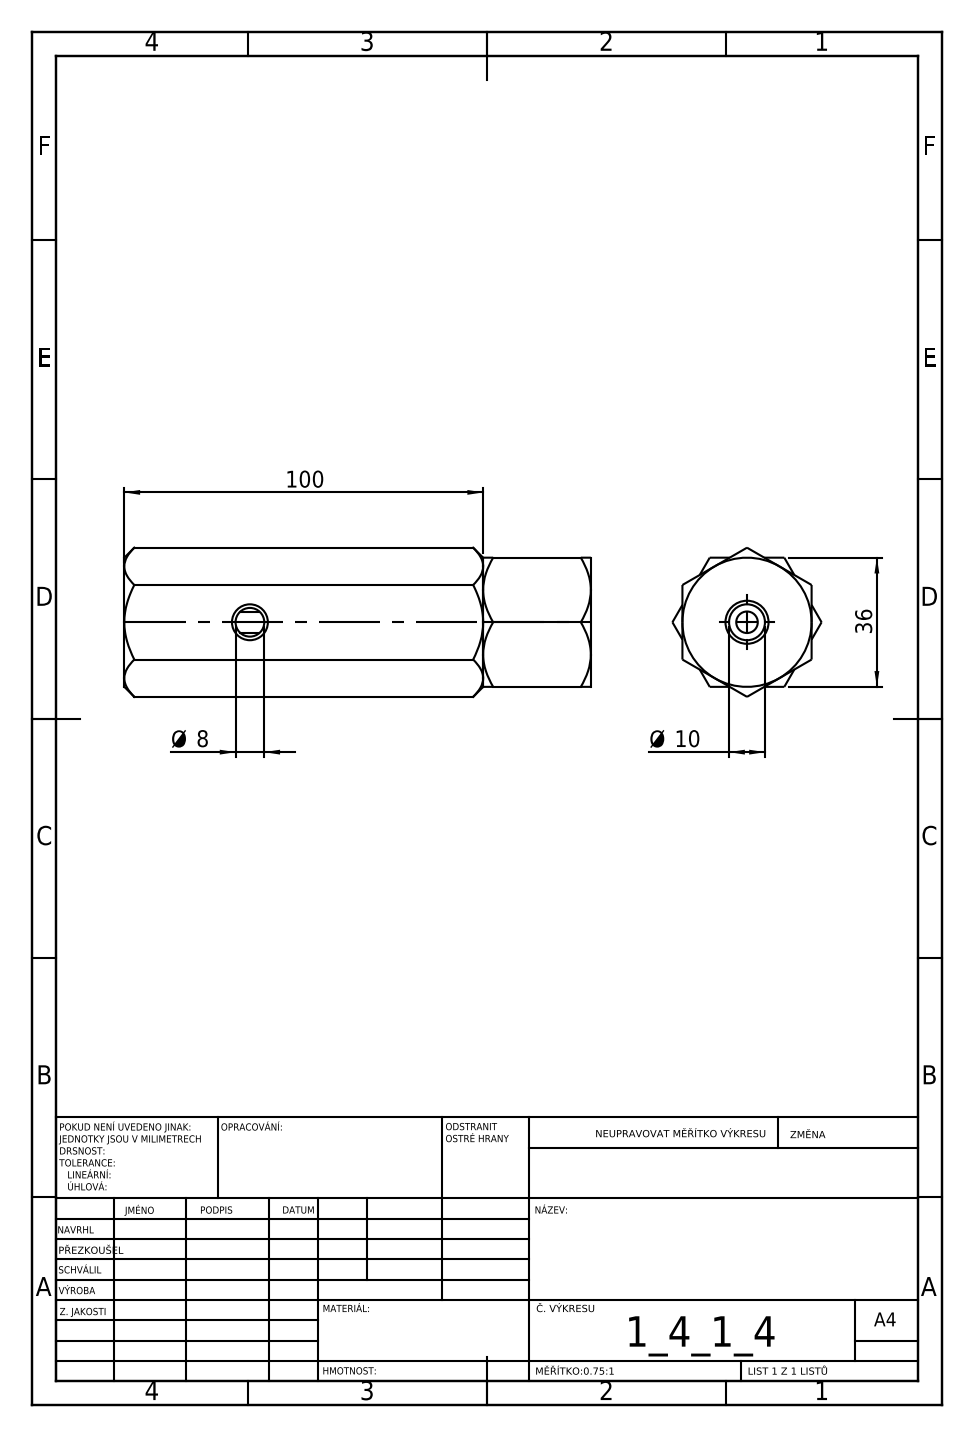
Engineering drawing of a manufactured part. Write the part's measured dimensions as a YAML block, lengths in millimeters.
step_written_by: "SolidWorks 2019 (CONFIG_CONTROL_DESIGN)"
units: millimeters
bodies: {solids: 2, faces: 59, planar: 19, cylindrical: 8, other: 32}
overall_size: [130, 41.57, 41.57]
volume: 138520
surface_area: 23531
round_holes:
  - {diameter: 6, count: 1}
  - {diameter: 8, count: 1}
  - {diameter: 10, count: 1}
face_to_face_distances: [36, 30, 130, 100, 110, 80, 20, 18]
